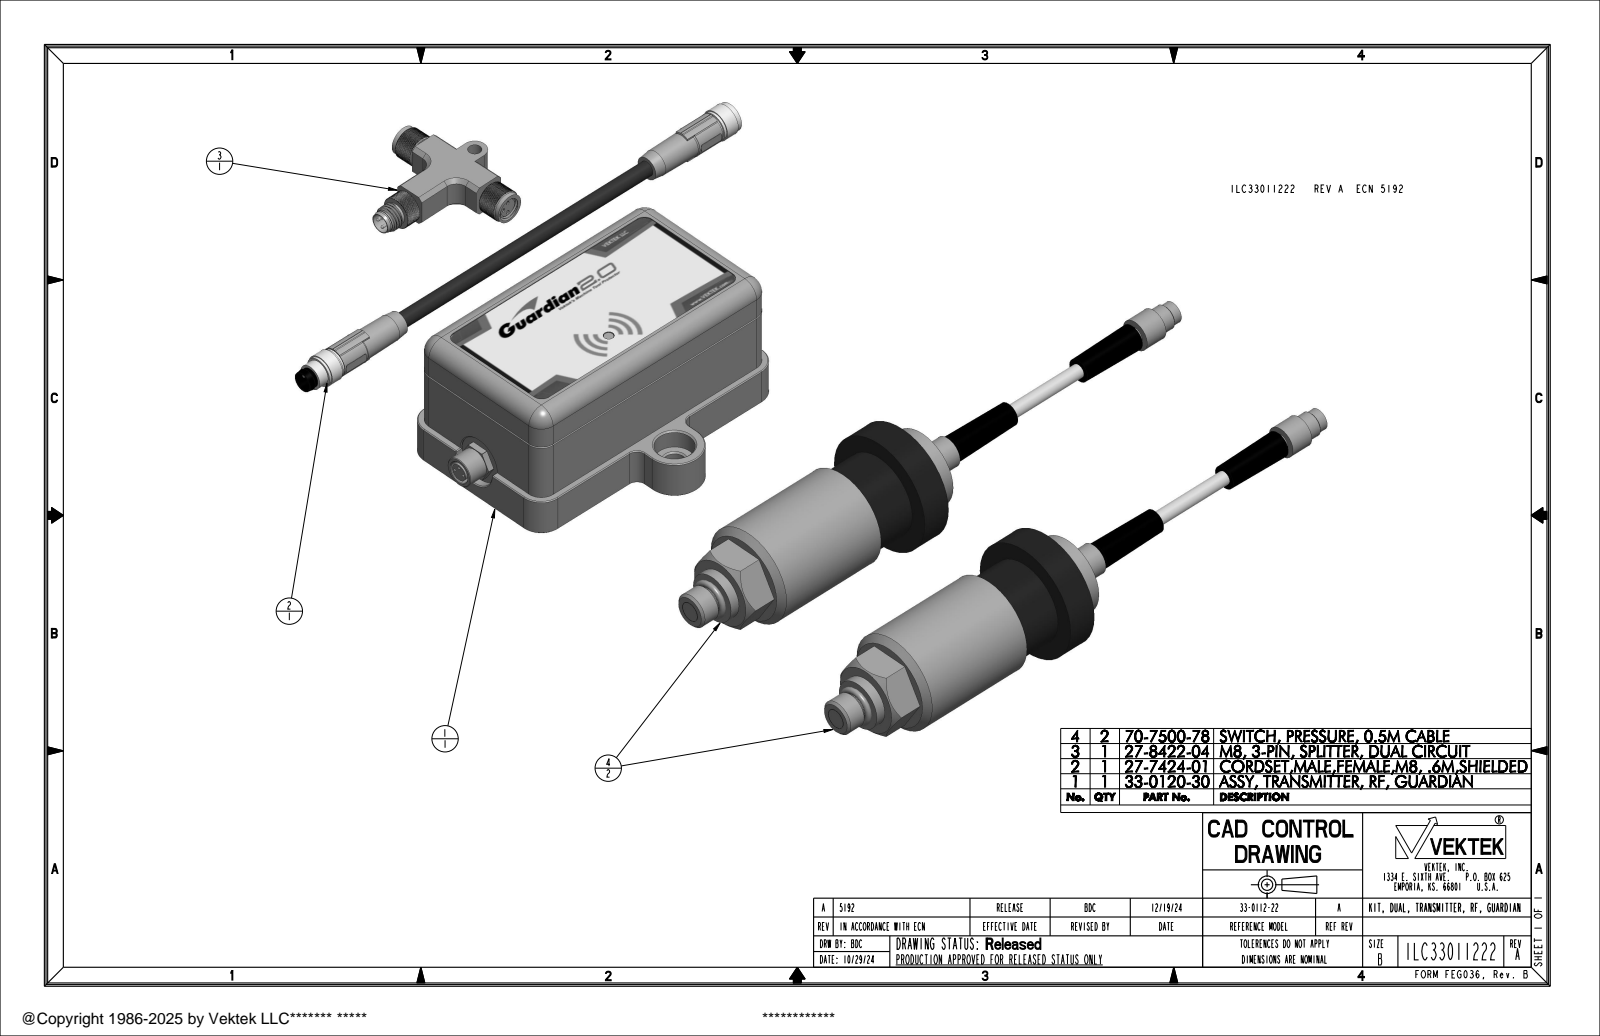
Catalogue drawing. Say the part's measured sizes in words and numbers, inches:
The part is named "27842204; 33012030P; 29950000; 33012030 (+3 more)". Its 3-D file was written by "CREO PARAMETRIC BY PTC INC, 2021164 (AUTOMOTIVE_DESIGN)". It is 7 solids with 1894 faces: 895 planar, 571 cylindrical and 428 other. Overall it measures 12.013 by 7.719 by 1.933 inches. Its volume is 22.14 cubic inches and its surface area 103.9 square inches. Round holes: 4 of diameter 0.138, 3 of diameter 0.031, 3 of diameter 0.039, 3 of diameter 0.047, 3 of diameter 0.276, 2 of diameter 0.25, 2 of diameter 0.467, 2 of diameter 0.472, 2 of diameter 0.875, 1 of diameter 0.13, 1 of diameter 0.165, 1 of diameter 0.224. Round bosses or shafts: 9 of diameter 0.039, 6 of diameter 0.048, 6 of diameter 0.038, 4 of diameter 0.22, 4 of diameter 0.118, 3 of diameter 0.315, 2 of diameter 1.5, 2 of diameter 1.25. Partial cylindrical surfaces (rounded edges, fillets, slot ends): 26 of radius 0.02, 8 of radius 0.118, 8 of radius 0.197, 4 of radius 0.211, 4 of radius 0.217, 4 of radius 0.276, 3 of radius 0.15, 3 of radius 0.193. The main face-to-face distances are 1.681, 0.079, 2.048, 2.126, 0.375, 3.623, 3.702, 0.375, 0.657, 0.282. The hole center spacings are 0.069, 0.098, 1.696, 3.963, 0.069, 2.811, 2.879, 2.947.
